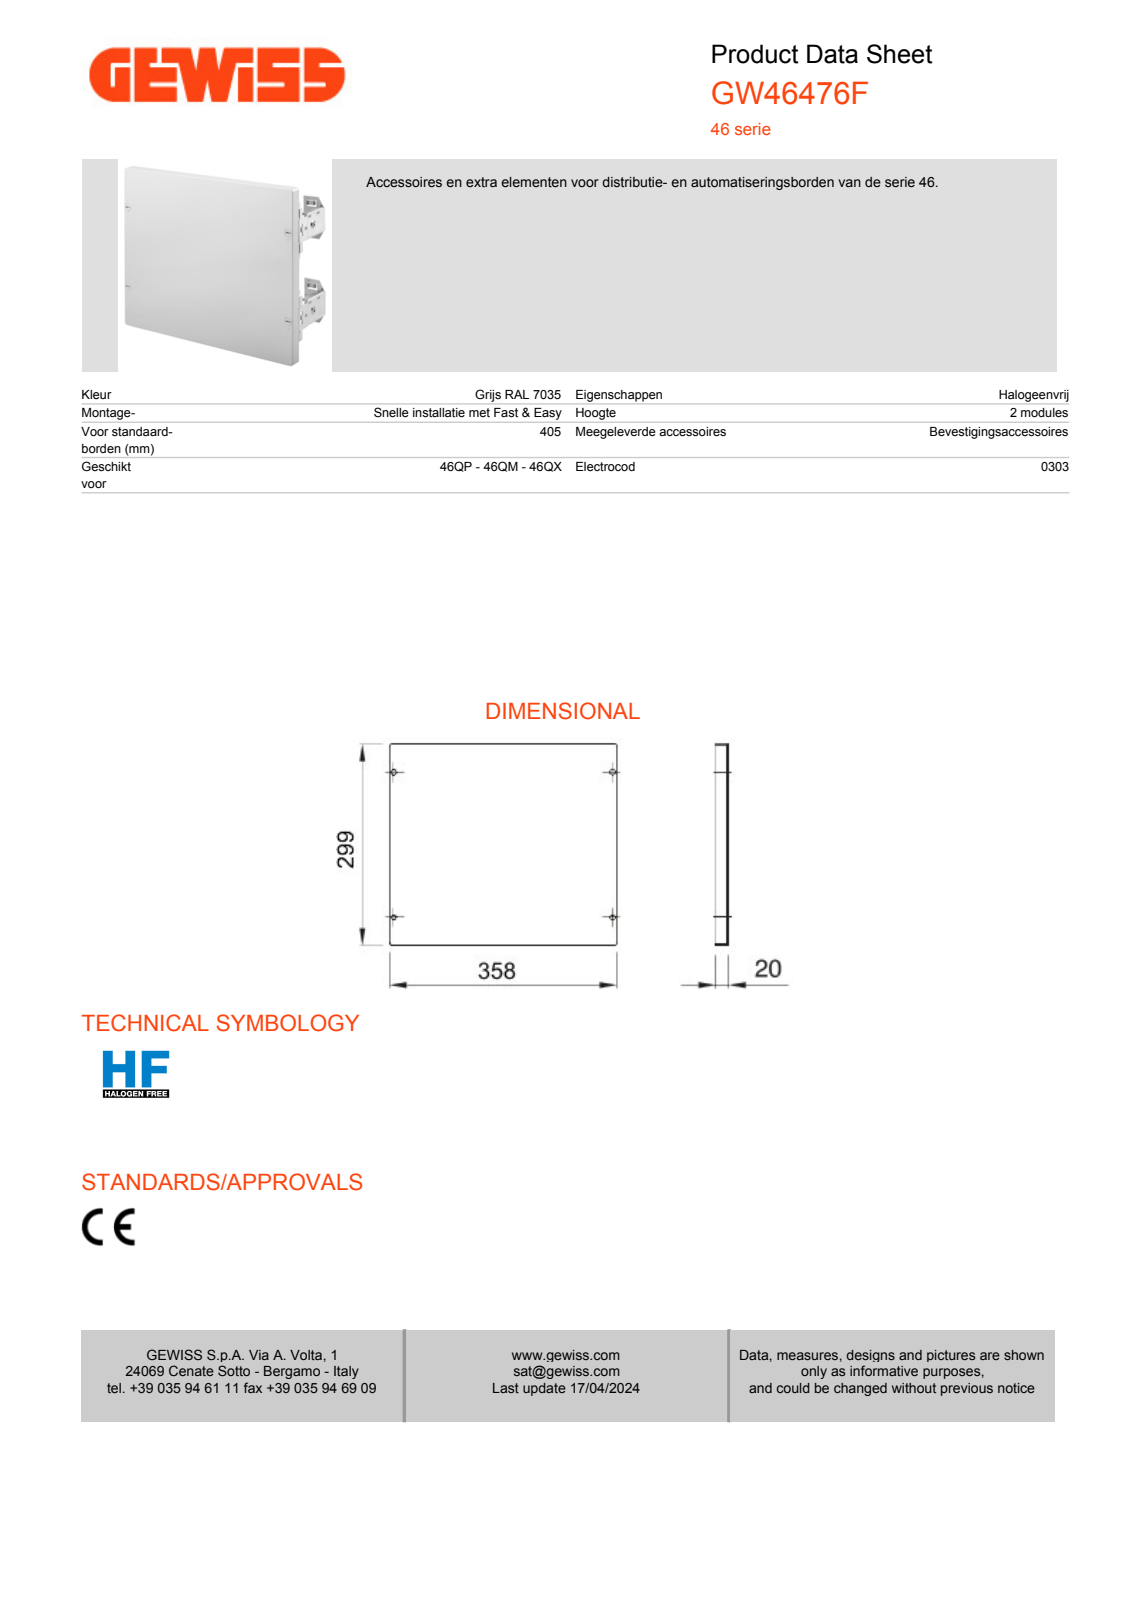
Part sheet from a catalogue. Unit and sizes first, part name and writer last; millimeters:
Units: millimetres
Overall size (bounding box): 363 × 299 × 119.87
Round holes (diameter × count): ⌀4.5 ×8, ⌀6.5 ×8, ⌀5.5 ×4, ⌀8 ×2
Round bosses / shafts (diameter × count): ⌀14.4 ×4, ⌀13.4 ×4, ⌀9.6 ×4
Partial cylindrical surfaces — rounded edges, fillets, slot ends (radius × count): R1.5 ×50, R1 ×40, R1.15 ×16, R0.5 ×8, R2 ×8, R1.25 ×4, R4.67 ×4, R5.6 ×4
Main face-to-face distances: 3, 1.5, 4, 353.5, 112, 113.5, 115, 110.5, 349.5, 17
Hole centre spacings: 150, 30.23, 35.11, 327.63, 342.07, 14.5, 60, 120.06
Volume: 460 488 mm³ · Surface area: 351 202 mm²
Bodies: 5 solids, 1130 faces (714 planar, 312 cylindrical, 104 other)
Part name (STEP PRODUCT): 55711006E2XX_MOSTRINA_CIECA_DOP; 55718951FXXX_STAFFA_X_SUPP_GUID; STAFFE_76_ASM; GW46476F_ASM
STEP written by: CREO PARAMETRIC BY PTC INC, 2020354 (CONFIG_CONTROL_DESIGN)
